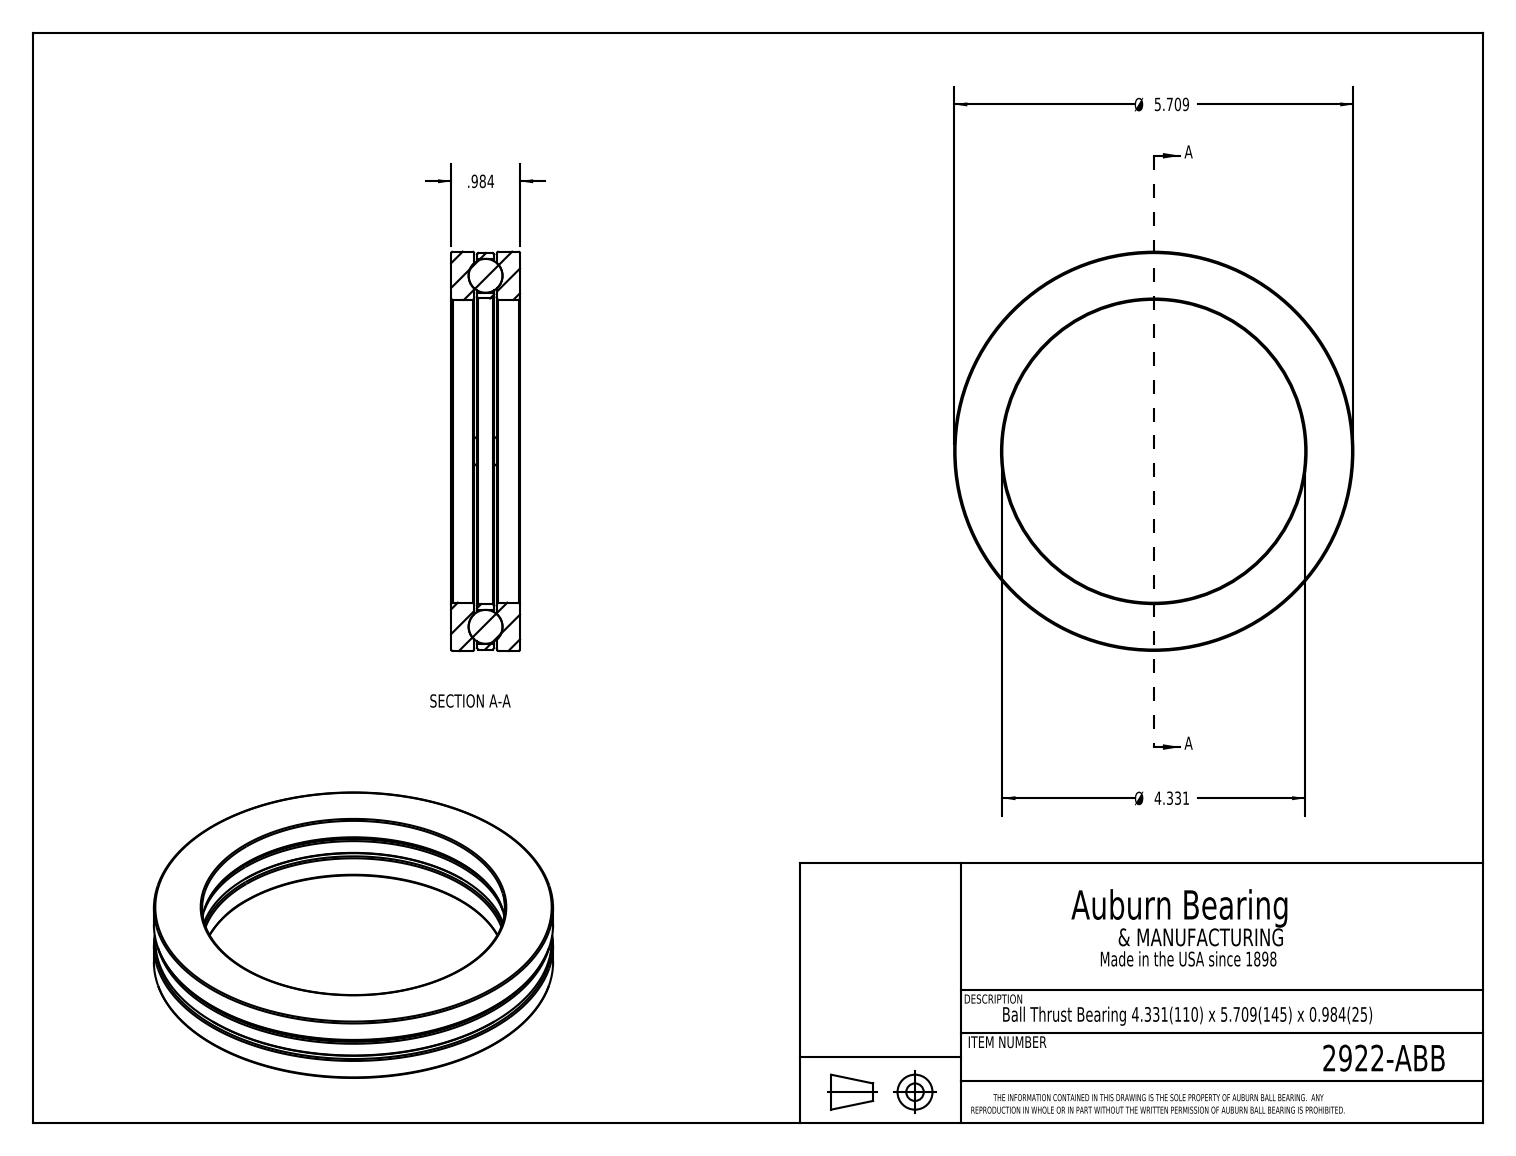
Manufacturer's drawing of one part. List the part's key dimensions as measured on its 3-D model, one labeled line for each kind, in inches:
Part name (STEP PRODUCT): 2922-ABB
STEP written by: SolidWorks 2017 (CONFIG_CONTROL_DESIGN)
Units: inches
Bodies: 7 solids, 36 faces (8 planar, 10 cylindrical, 18 other)
Overall size (bounding box): 5.709 × 5.709 × 0.984
Volume: 9.066 in³ · Surface area: 94.89 in²
Round holes (diameter × count): ⌀0.494 ×4, ⌀4.331 ×1, ⌀4.371 ×1
Round bosses / shafts (diameter × count): ⌀5.709 ×1, ⌀5.669 ×1
Main face-to-face distances: 0.369, 0.615, 0.984, 0.328, 0.656, 0.041, 0.287, 0.246, 0.328
Hole centre spacings: 2.51, 3.55, 5.02
